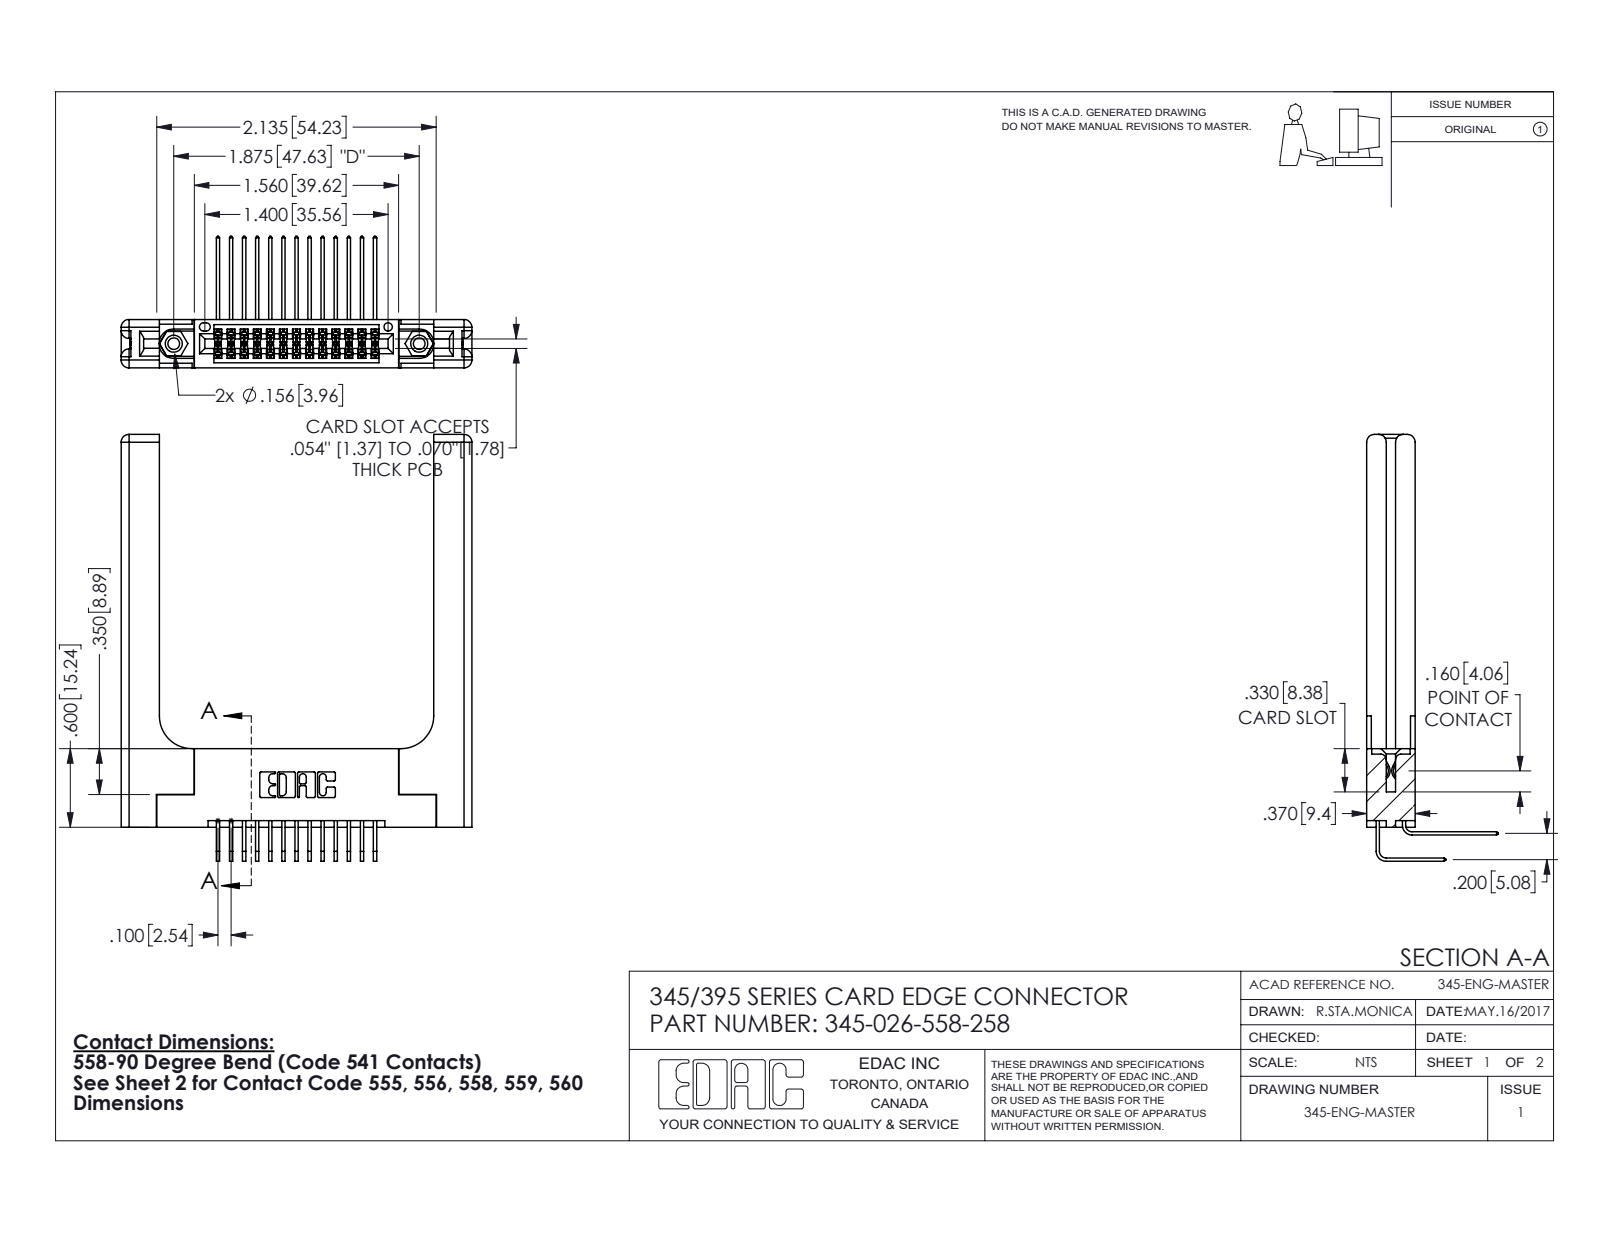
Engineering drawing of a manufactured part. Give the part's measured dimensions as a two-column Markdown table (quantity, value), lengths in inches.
| quantity | value |
| --- | --- |
| part name | 345-250-001_345-250-001-102; 345-026-558-258; 345-220-058_345-220-058; 345-292-001_558 Tail - 2 (+2 more) |
| STEP written by | SolidWorks 2016 (CONFIG_CONTROL_DESIGN) |
| units | inches |
| bodies | 31 solids, 1734 faces (1138 planar, 536 cylindrical, 60 other) |
| overall size | 3.259 × 2.679 × 1.005 |
| volume | 0.913 in³ |
| surface area | 22.94 in² |
| round holes (diameter × count) | 0.089 × 2, 0.125 × 2, 0.156 × 2, 0.064 × 1 |
| round bosses / shafts (diameter × count) | 0.155 × 2 |
| partial cylindrical surfaces (radius × count) | 0.006 × 52, 0.01 × 22, 0.06 × 16, 0.007 × 6, 0.031 × 6, 0.026 × 3, 0.014 × 2, 0.019 × 2 |
| main face-to-face distances | 0.37, 0.072, 0.2, 0.298, 0.077, 0.148, 0.15, 0.22, 0.225, 0.098 |
| hole center spacings | 0.27, 1.643, 1.875 |
